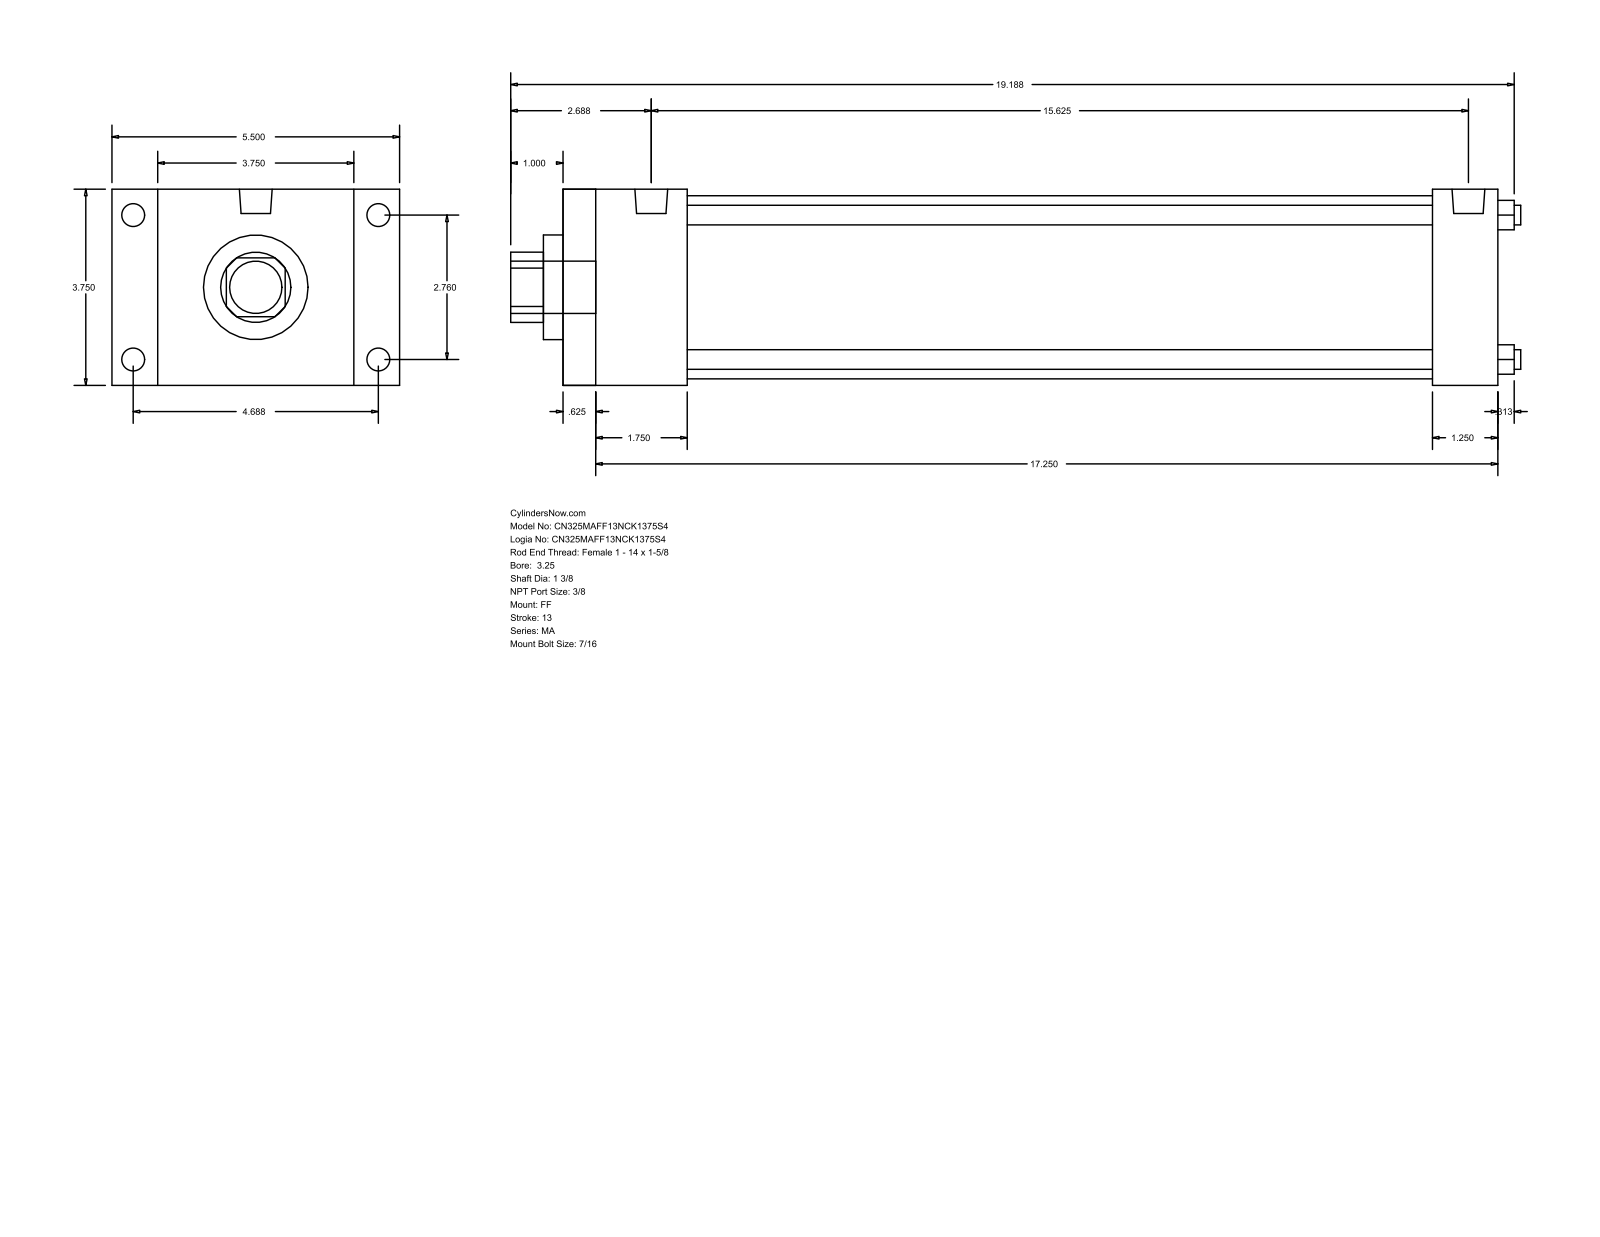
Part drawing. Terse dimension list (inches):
name: MA_FF__0325_1.375
written by: GSSL Pune (CONFIG_CONTROL_DESIGN)
unit: in
bodies: 0 solids, 92 faces (64 planar, 28 cylindrical, 0 other)
size: 19.313 × 5.5 × 3.75
holes: 4× ⌀0.375, 1× ⌀1.375, 1× ⌀2, 1× ⌀3.5
bosses: 8× ⌀0.437, 2× ⌀0.627, 1× ⌀1
rounds: 1× R0.672
face distances: 3.75, 17.875, 0.625, 17.25, 0.875, 4.625, 2.375, 16.625, 1.75, 16
hole spacings: 1.952, 2.76, 3.903
